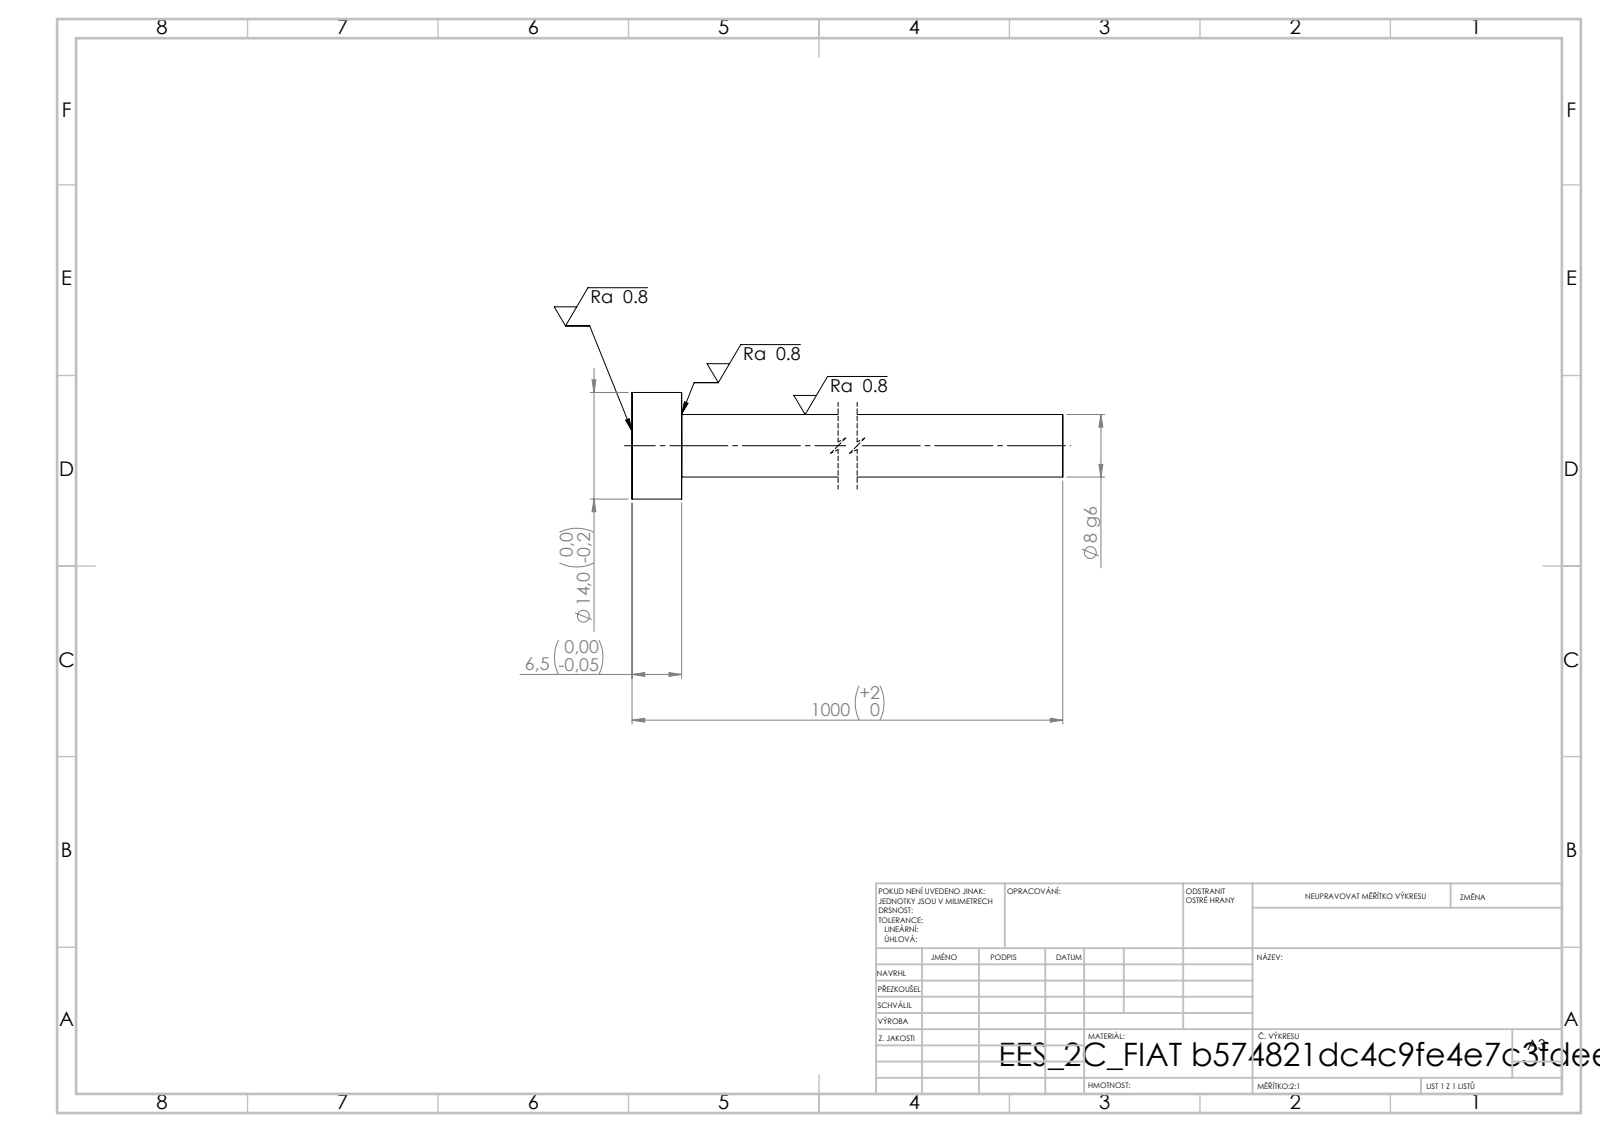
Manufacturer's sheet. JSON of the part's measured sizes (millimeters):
{"step_written_by": "SolidWorks 2019 (CONFIG_CONTROL_DESIGN)", "units": "millimeters", "bodies": {"solids": 1, "faces": 7, "planar": 3, "cylindrical": 4, "other": 0}, "overall_size": [1000, 14, 14], "volume_mm3": 53468, "surface_area_mm2": 26187, "round_bosses_or_shafts": [[14, 1], [8.2, 1]], "face_to_face_distances": [6.5, 1000, 993.5]}
